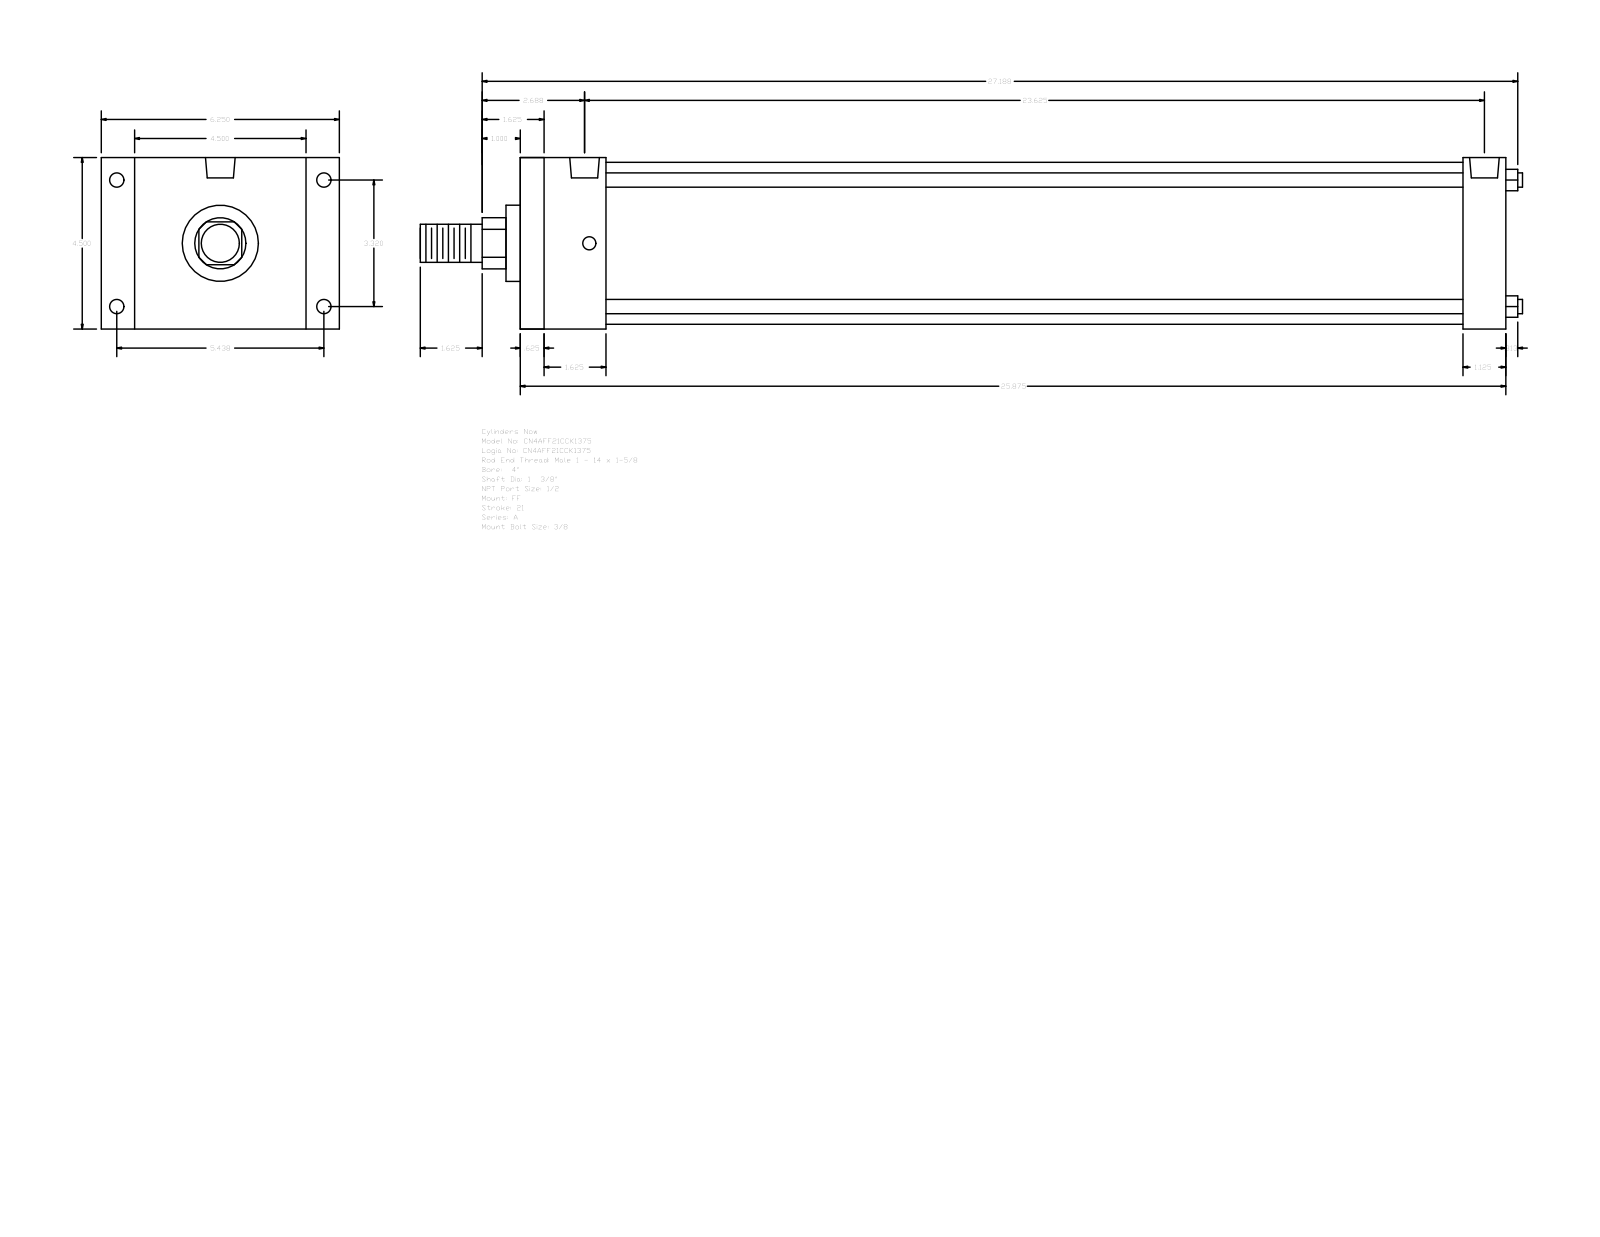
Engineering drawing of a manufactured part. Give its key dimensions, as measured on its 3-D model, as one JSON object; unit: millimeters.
{"part_name": "A_FF__0400_1.375", "step_written_by": "GSSL Pune (CONFIG_CONTROL_DESIGN)", "units": "millimeters", "bodies": {"solids": 0, "faces": 92, "planar": 64, "cylindrical": 28, "other": 0}, "overall_size": [735.01, 158.75, 114.3], "round_holes": [[8.73, 4], [9.53, 4], [19.77, 2]], "round_bosses_or_shafts": [[9.53, 4], [107.95, 1], [50.8, 1], [34.92, 1], [25.4, 1]], "partial_cylinders_radius": [[17.06, 1]], "face_to_face_distances": [114.3, 657.22, 641.35, 15.87, 57.15, 28.57, 22.23, 136.53, 628.65, 612.78], "hole_center_spacings": [3.18, 84.32, 138.12, 161.82, 593.72, 596.9, 600.08]}
